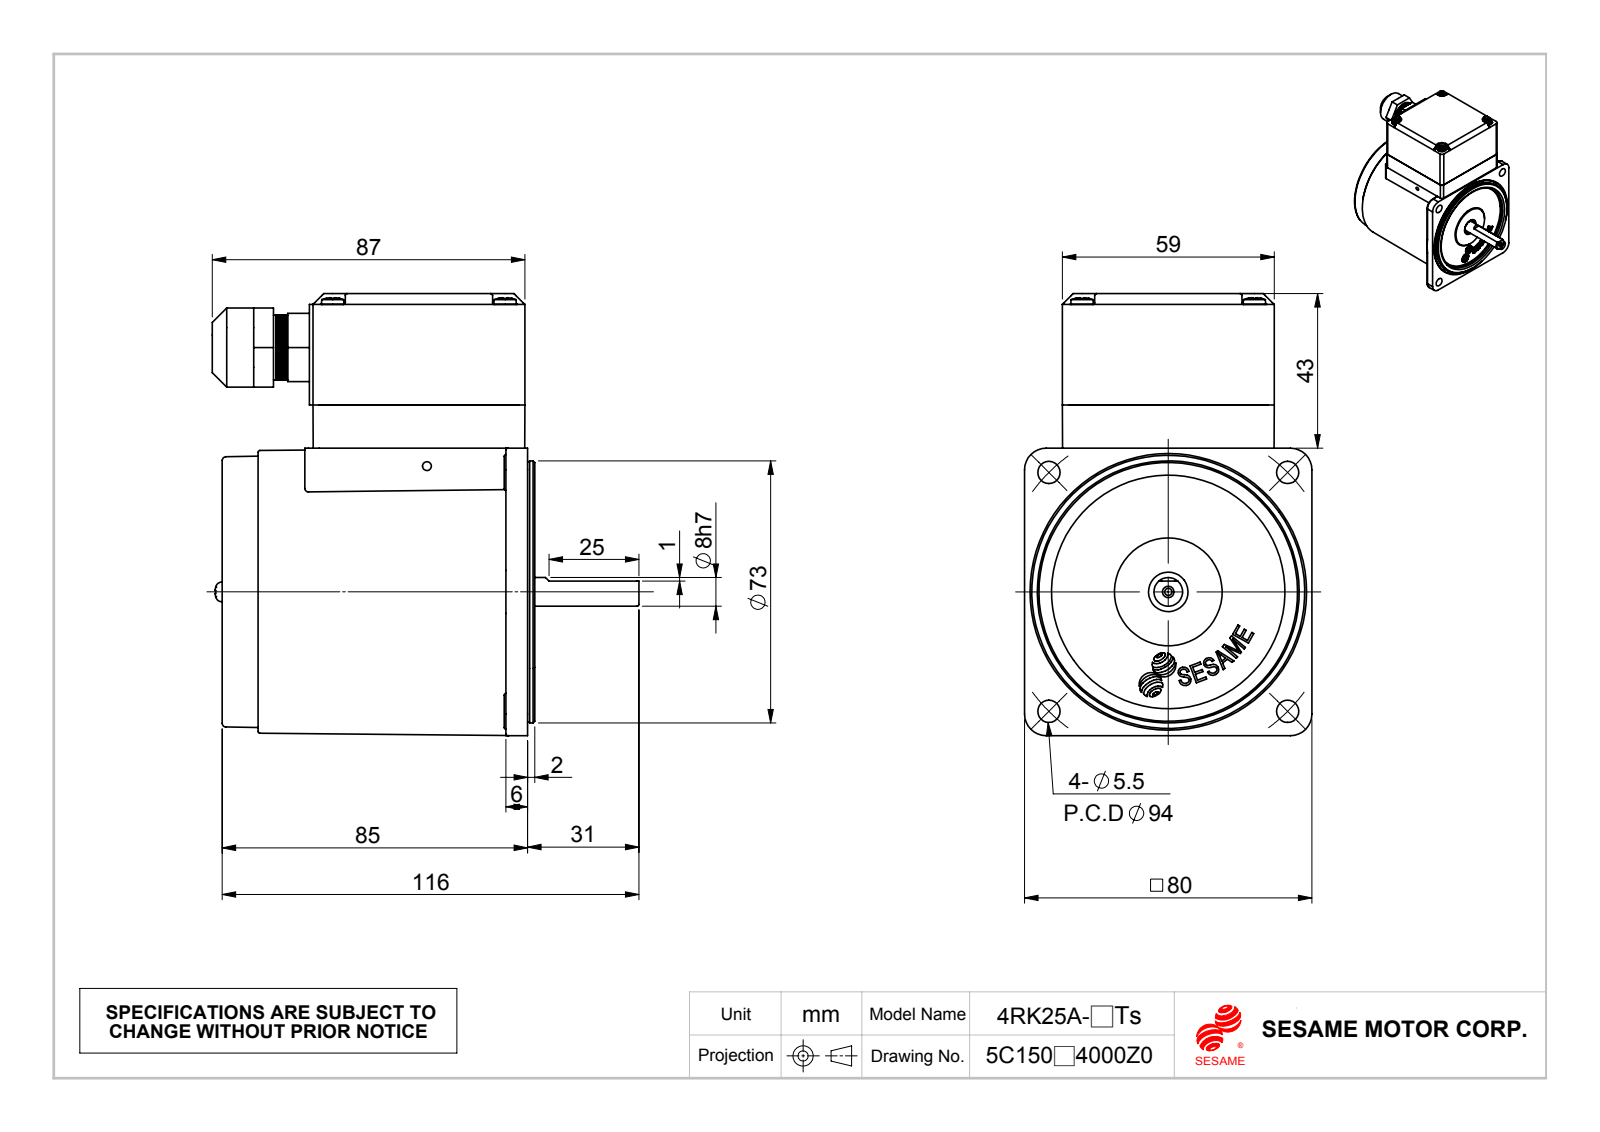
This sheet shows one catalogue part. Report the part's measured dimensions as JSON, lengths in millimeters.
{"part_name": "25A_3.研磨; 펥짰웰찿M4즤40x1t_Default; 成品180度; M425TsA-RK_鑽孔攻牙 (+2 more)", "step_written_by": "SolidWorks 2010 (CONFIG_CONTROL_DESIGN)", "units": "millimeters", "bodies": {"solids": 14, "faces": 2713, "planar": 304, "cylindrical": 967, "other": 1442}, "overall_size": [123, 118.75, 80], "volume_mm3": 251288, "surface_area_mm2": 105653, "round_holes": [[3.3, 4], [3.5, 4], [3.9, 4], [4.2, 4], [4.3, 4], [6.2, 4], [2.5, 3], [4, 2], [11, 2], [2, 1], [12, 1], [14.5, 1]], "round_bosses_or_shafts": [[3, 6], [6.3, 4], [5.5, 2], [72.93, 1], [72.53, 1], [40, 1], [37, 1], [22, 1]], "partial_cylinders_radius": [[0.5, 12], [2, 12], [0.3, 8], [0.61, 8], [1.16, 8], [1.29, 8], [2.26, 8], [4, 6]], "face_to_face_distances": [12, 1, 84, 1.5, 82.5, 0.5, 3, 0.75, 80, 83.5], "hole_center_spacings": [49.33, 15, 11.48, 21.22, 27.72, 31.99, 37.9, 46.99]}
